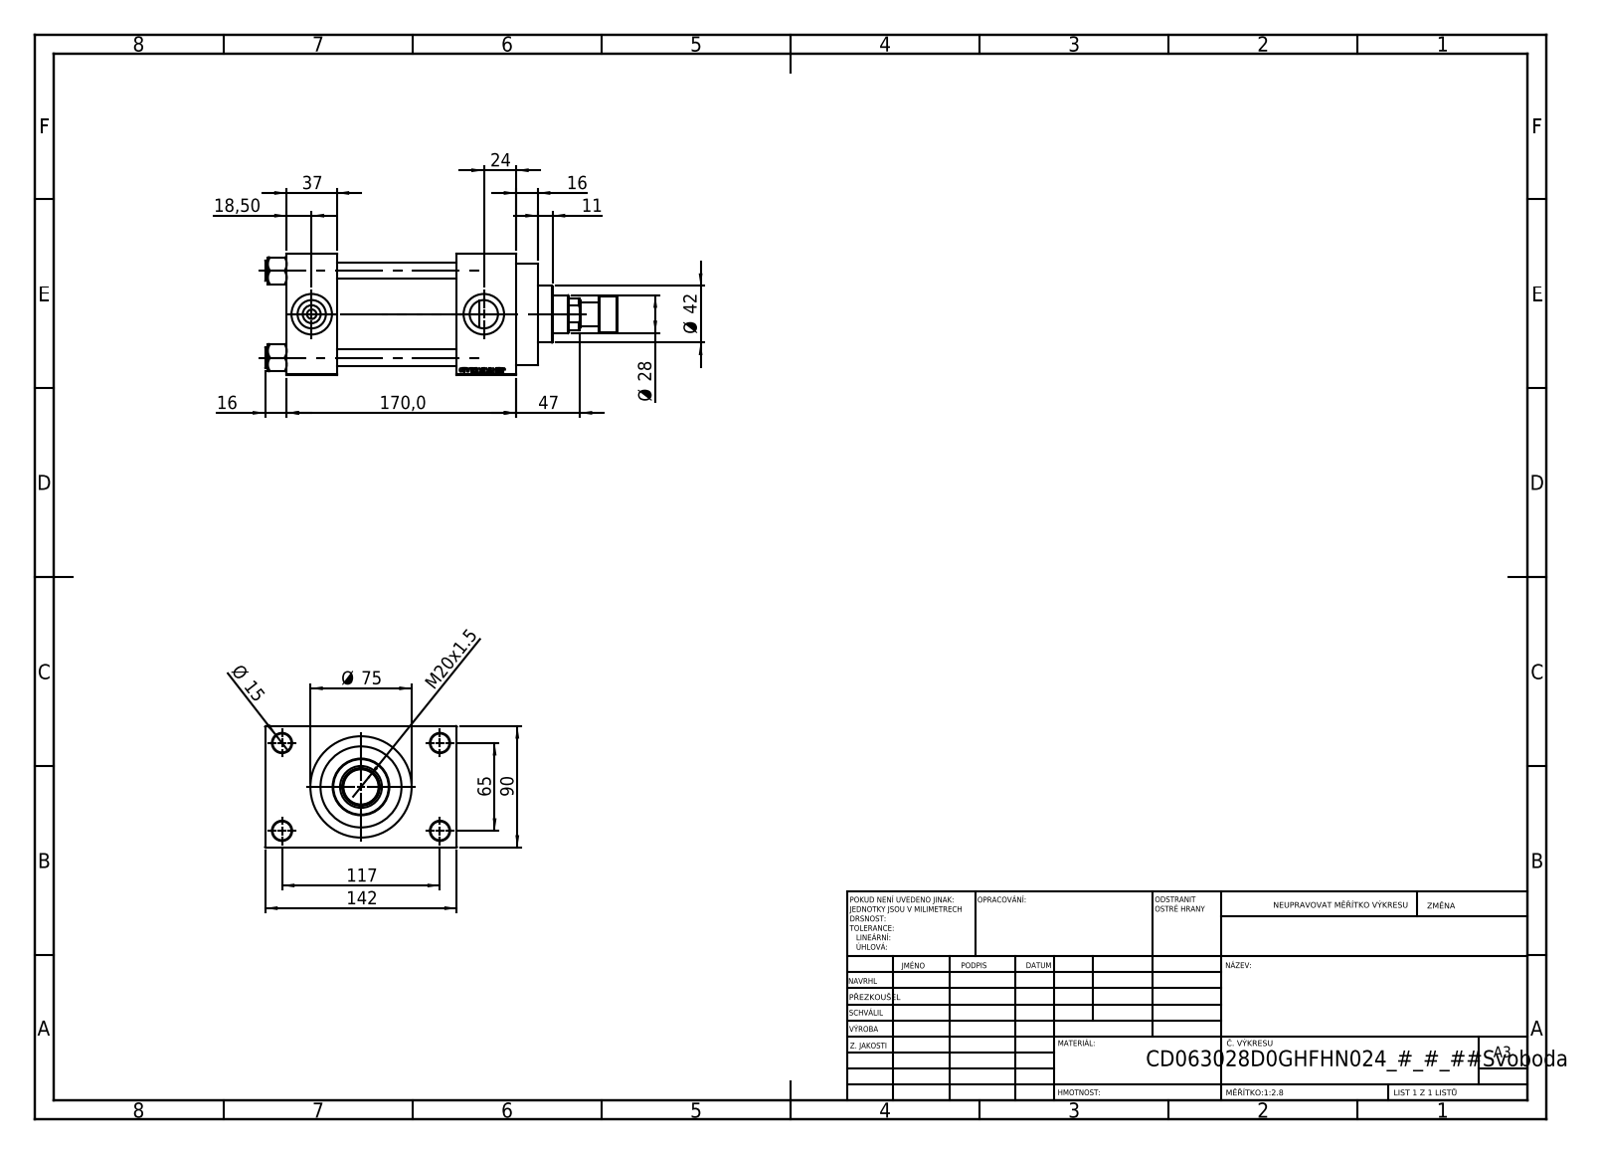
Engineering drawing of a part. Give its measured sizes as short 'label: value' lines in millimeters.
name: V215CR_ROD_END_F; V215CD_VC_A; V215CD_NUT_M5_D; V215CD_VCP_D (+2 more)
written by: SolidWorks 2019 (CONFIG_CONTROL_DESIGN)
unit: mm
bodies: 12 solids, 1117 faces (501 planar, 92 cylindrical, 524 other)
size: 261 × 142 × 90
volume: 1 159 000 mm³; area: 223 174 mm²
holes: 4× ⌀12, 4× ⌀14, 2× ⌀7, 2× ⌀20.96, 2× ⌀30, 1× ⌀18.5, 1× ⌀28, 1× ⌀31, 1× ⌀50, 1× ⌀60, 1× ⌀63
bosses: 4× ⌀15, 1× ⌀75, 1× ⌀69, 1× ⌀42, 1× ⌀27, 1× ⌀18
face distances: 90, 89, 37, 126, 133, 170, 44, 26, 116, 142
hole spacings: 26.35, 45.47, 64.3, 66.92, 69.81, 90.65, 111.34, 65
